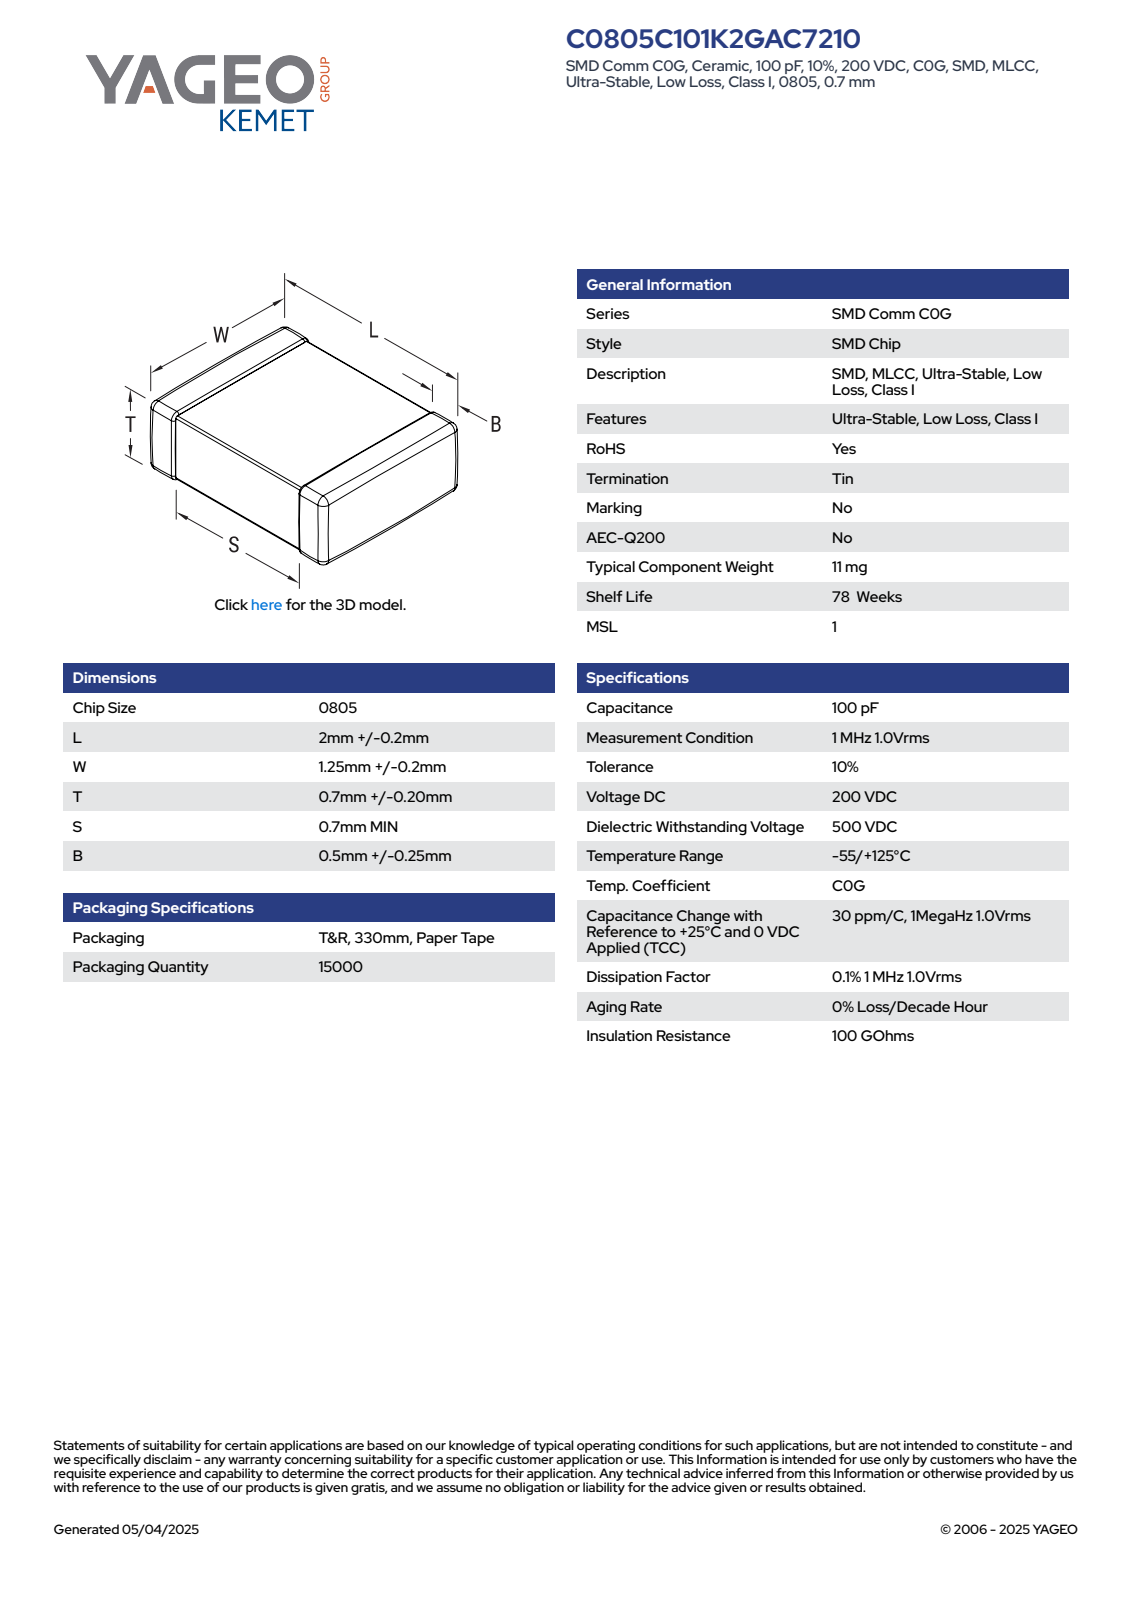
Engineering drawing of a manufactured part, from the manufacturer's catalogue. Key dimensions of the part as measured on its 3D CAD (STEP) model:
Part name (STEP PRODUCT): CCS_CCSTD_0805_L2.2W1.45T0.9B0.5
STEP written by: SolidWorks 2021 (AUTOMOTIVE_DESIGN)
Units: millimetres
Bodies: 4 solids, 121 faces (71 planar, 34 cylindrical, 16 other)
Overall size (bounding box): 2.2 × 1.45 × 0.9
Volume: 3 mm³ · Surface area: 13 mm²
Main face-to-face distances: 0.87, 0.9, 2.2, 1.45, 1.42, 0.84, 1.39, 0.97, 1.23, 1.19
